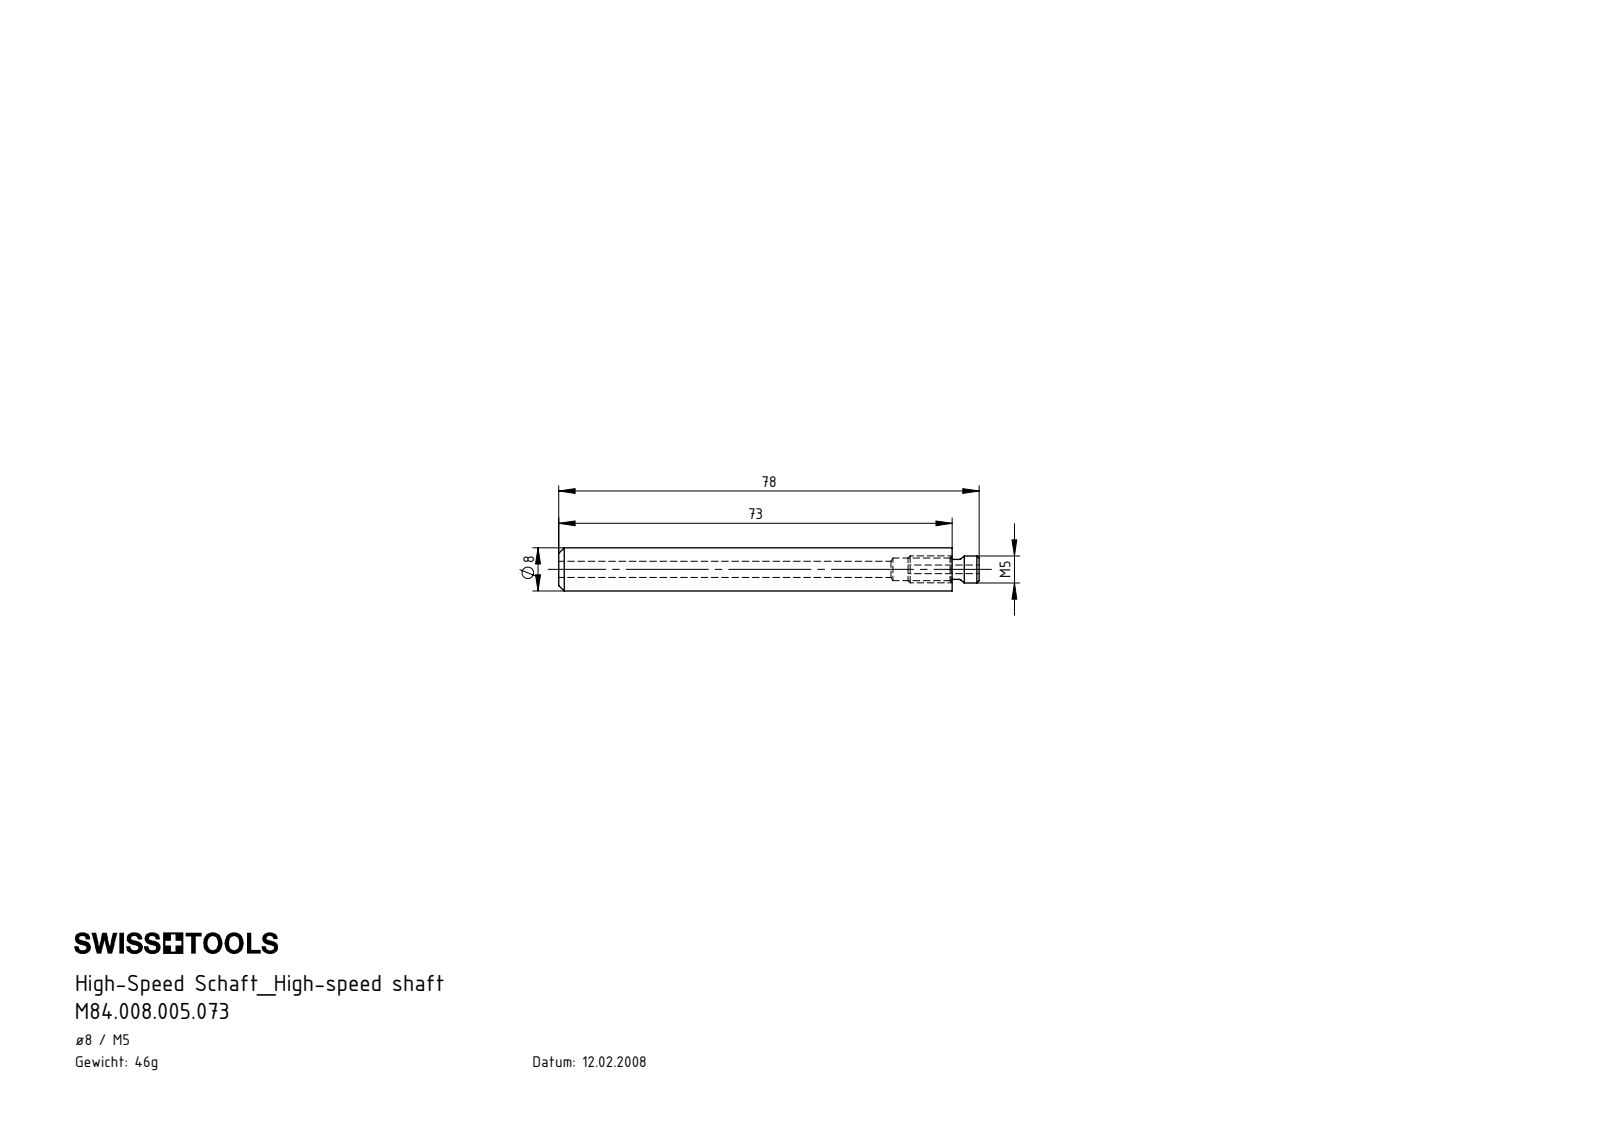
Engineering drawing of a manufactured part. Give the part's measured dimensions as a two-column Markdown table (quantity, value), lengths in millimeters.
| quantity | value |
| --- | --- |
| part name | HM1-BG1.005.013_A; HM1-U08.001.073_A; 8-H.5.K01.073_A |
| STEP written by | SolidWorks 2017 (AUTOMOTIVE_DESIGN) |
| units | millimeters |
| bodies | 2 solids, 20 faces (5 planar, 7 cylindrical, 8 other) |
| overall size | 78 × 8 × 8 |
| volume | 3 277 mm³ |
| surface area | 2 932 mm² |
| round holes (diameter × count) | 1.6 × 1, 3 × 1, 4.2 × 1 |
| round bosses / shafts (diameter × count) | 8 × 1, 5 × 1, 3.7 × 1 |
| main face-to-face distances | 73, 64.8, 78, 8.2, 13.2, 5, 72.8, 8, 5.2 |
